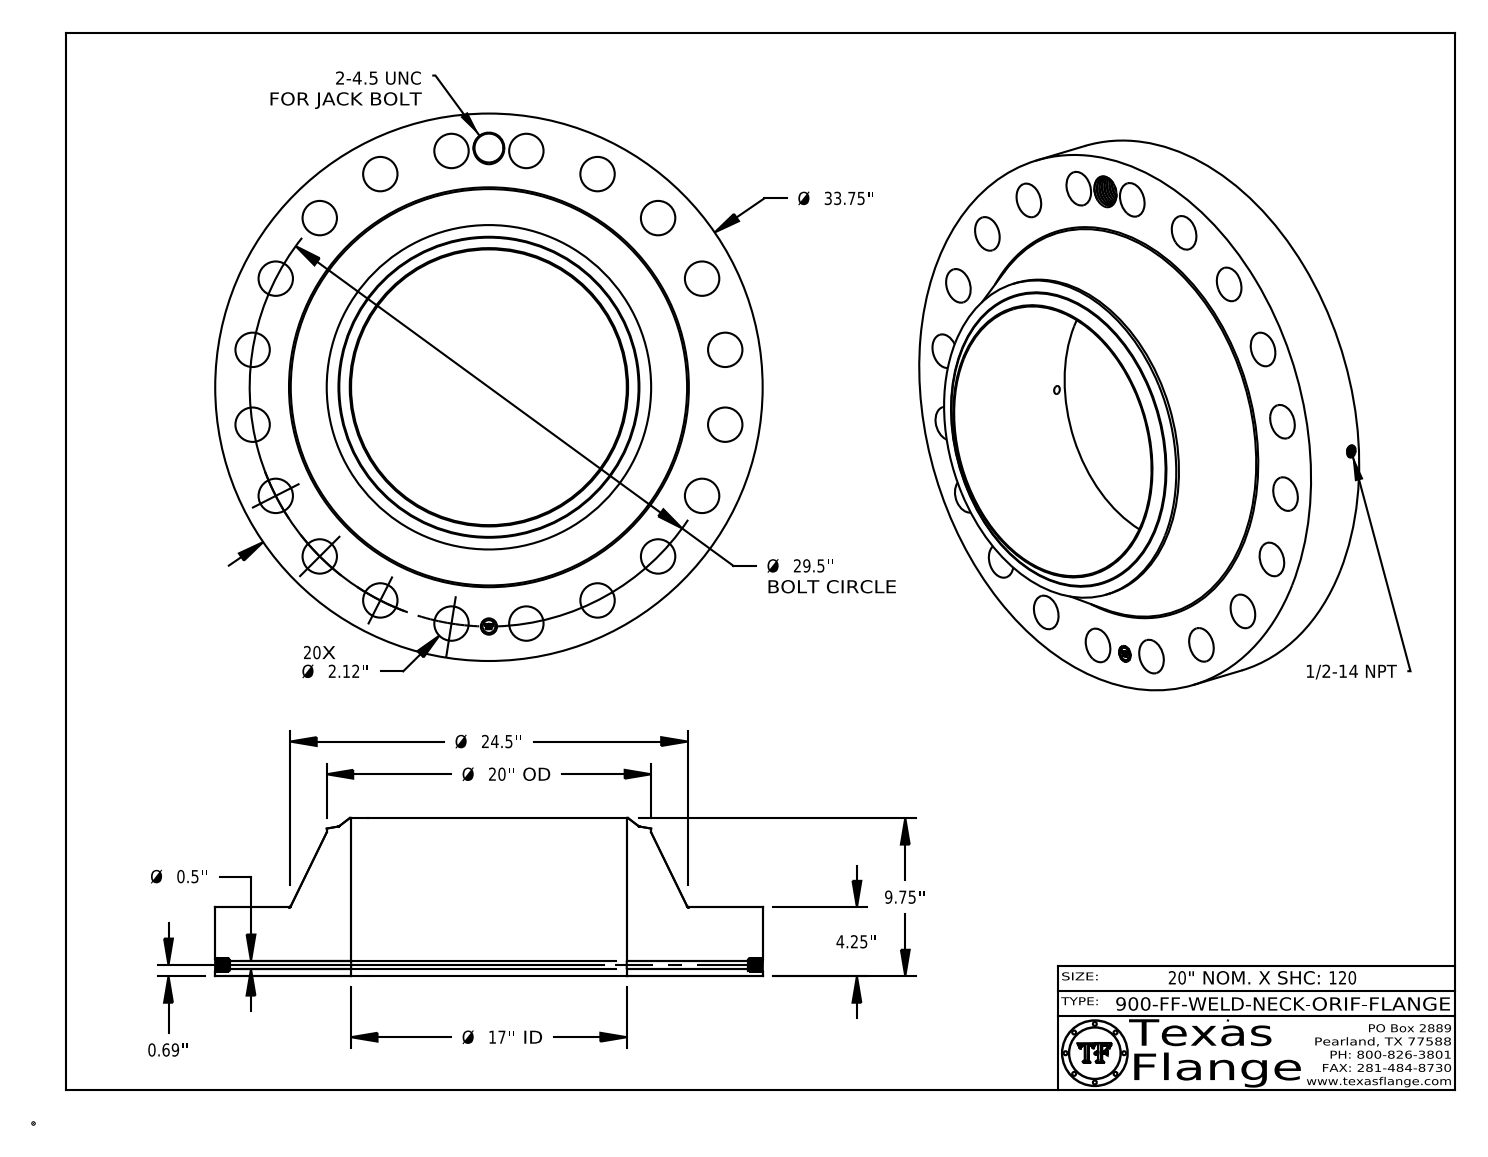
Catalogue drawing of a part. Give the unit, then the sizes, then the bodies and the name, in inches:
Units: inches
Overall size (bounding box): 33.75 × 33.75 × 9.75
Round holes (diameter × count): ⌀2.12 ×20, ⌀0.5 ×1, ⌀0.672 ×1, ⌀1 ×1, ⌀1.781 ×1, ⌀17 ×1
Round bosses / shafts (diameter × count): ⌀0.061 ×8, ⌀33.75 ×1, ⌀20 ×1, ⌀0.788 ×1
Main face-to-face distances: 4.25, 9.75, 5.5, 4.235, 0.015, 5.515, 0.298, 0.293, 0.054, 0.248
Hole centre spacings: 4.615, 9.116, 13.393, 17.34, 20.86, 23.866, 26.285, 29.137
Volume: 3 316 in³ · Surface area: 3 017 in²
Bodies: 1 solid, 819 faces (368 planar, 124 cylindrical, 327 other)
Part name (STEP PRODUCT): 900-FF-WELD-NECK
STEP written by: CATIA V5 STEP AP214 (AUTOMOTIVE_DESIGN)
